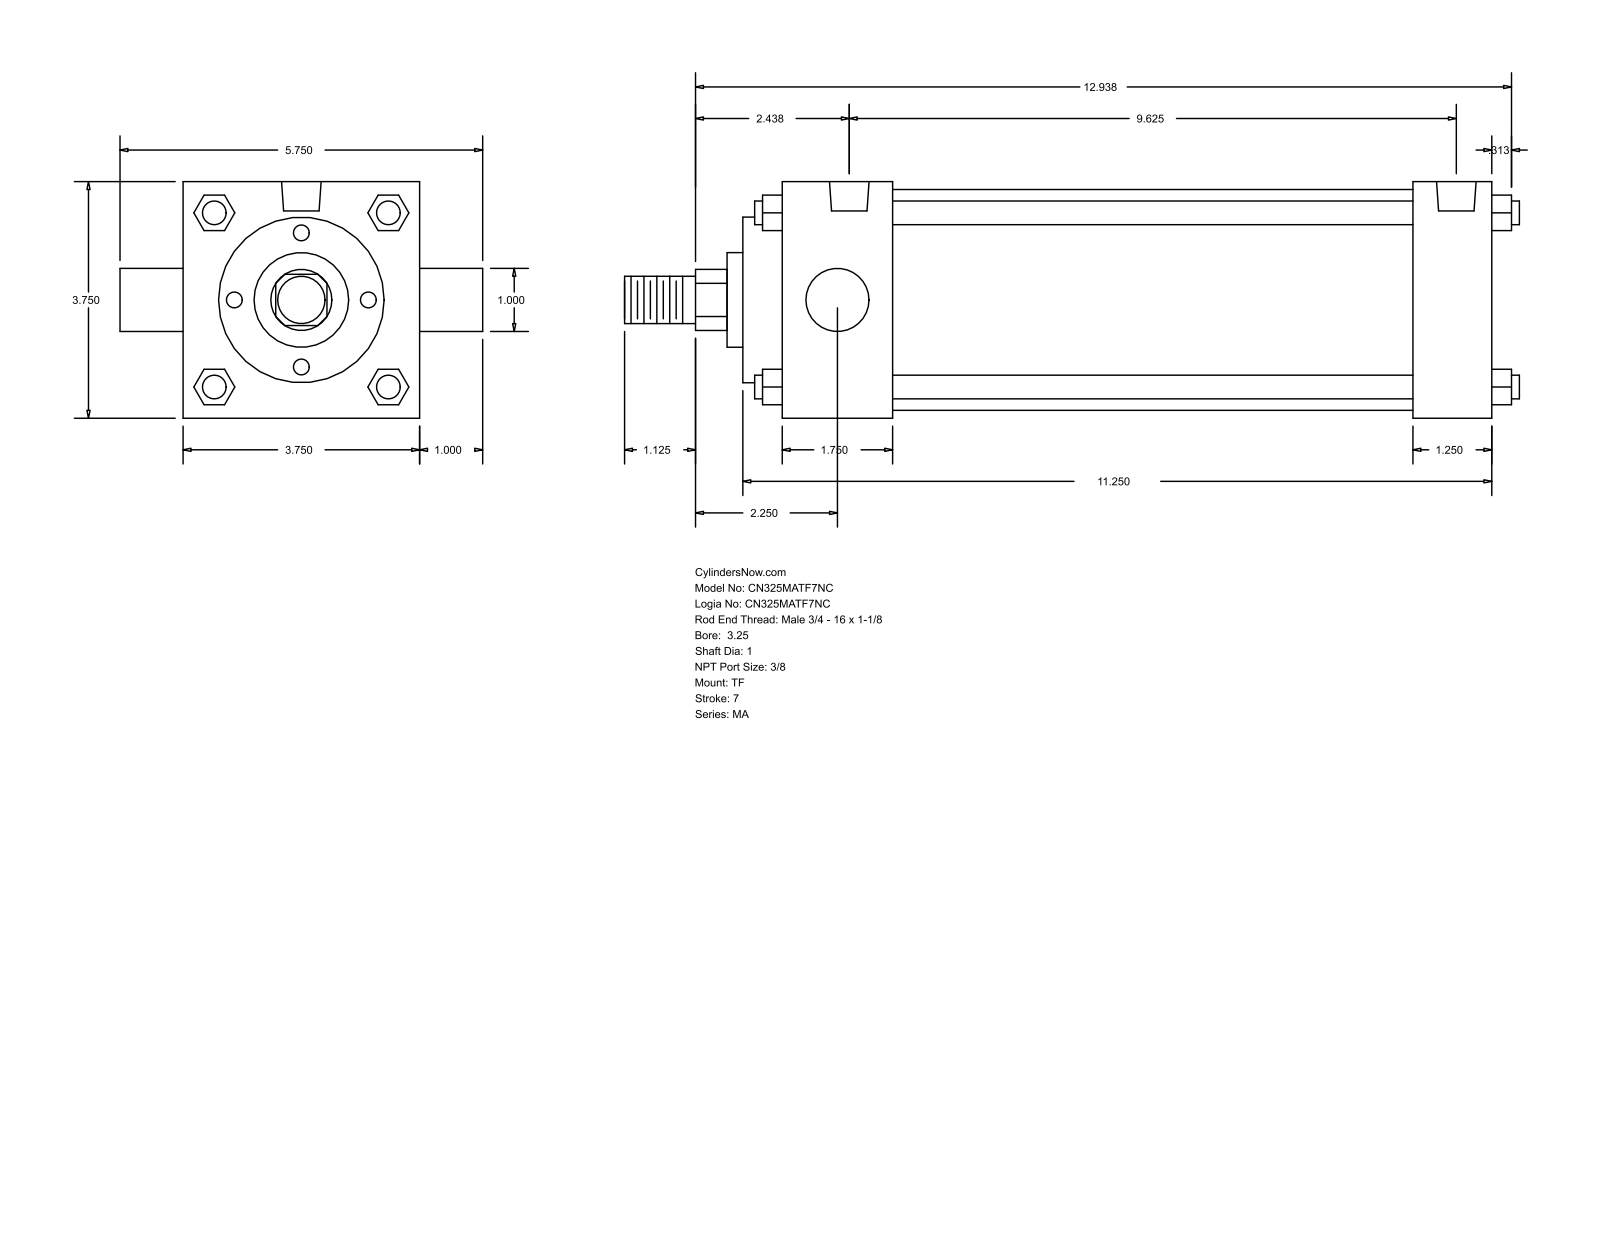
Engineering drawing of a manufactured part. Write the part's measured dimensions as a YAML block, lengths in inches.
part_name: "MA_TF__0325_1"
step_written_by: "GSSL Pune (CONFIG_CONTROL_DESIGN)"
units: inches
bodies: {solids: 0, faces: 122, planar: 93, cylindrical: 29, other: 0}
overall_size: [14.187, 5.75, 3.75]
round_holes:
  - {diameter: 0.437, count: 3}
  - {diameter: 0.627, count: 2}
round_bosses_or_shafts:
  - {diameter: 0.375, count: 4}
  - {diameter: 1, count: 2}
  - {diameter: 3.5, count: 1}
  - {diameter: 2.625, count: 1}
  - {diameter: 1.5, count: 1}
  - {diameter: 0.75, count: 1}
partial_cylinders:
  - {radius: 0.484, count: 1}
face_to_face_distances: [3.75, 11.25, 1.75, 10, 8.25, 9.5, 1.25, 0.625, 2.375, 10.625]
hole_center_spacings: [0.187, 0.188, 9.25, 9.437, 9.438, 9.625]
